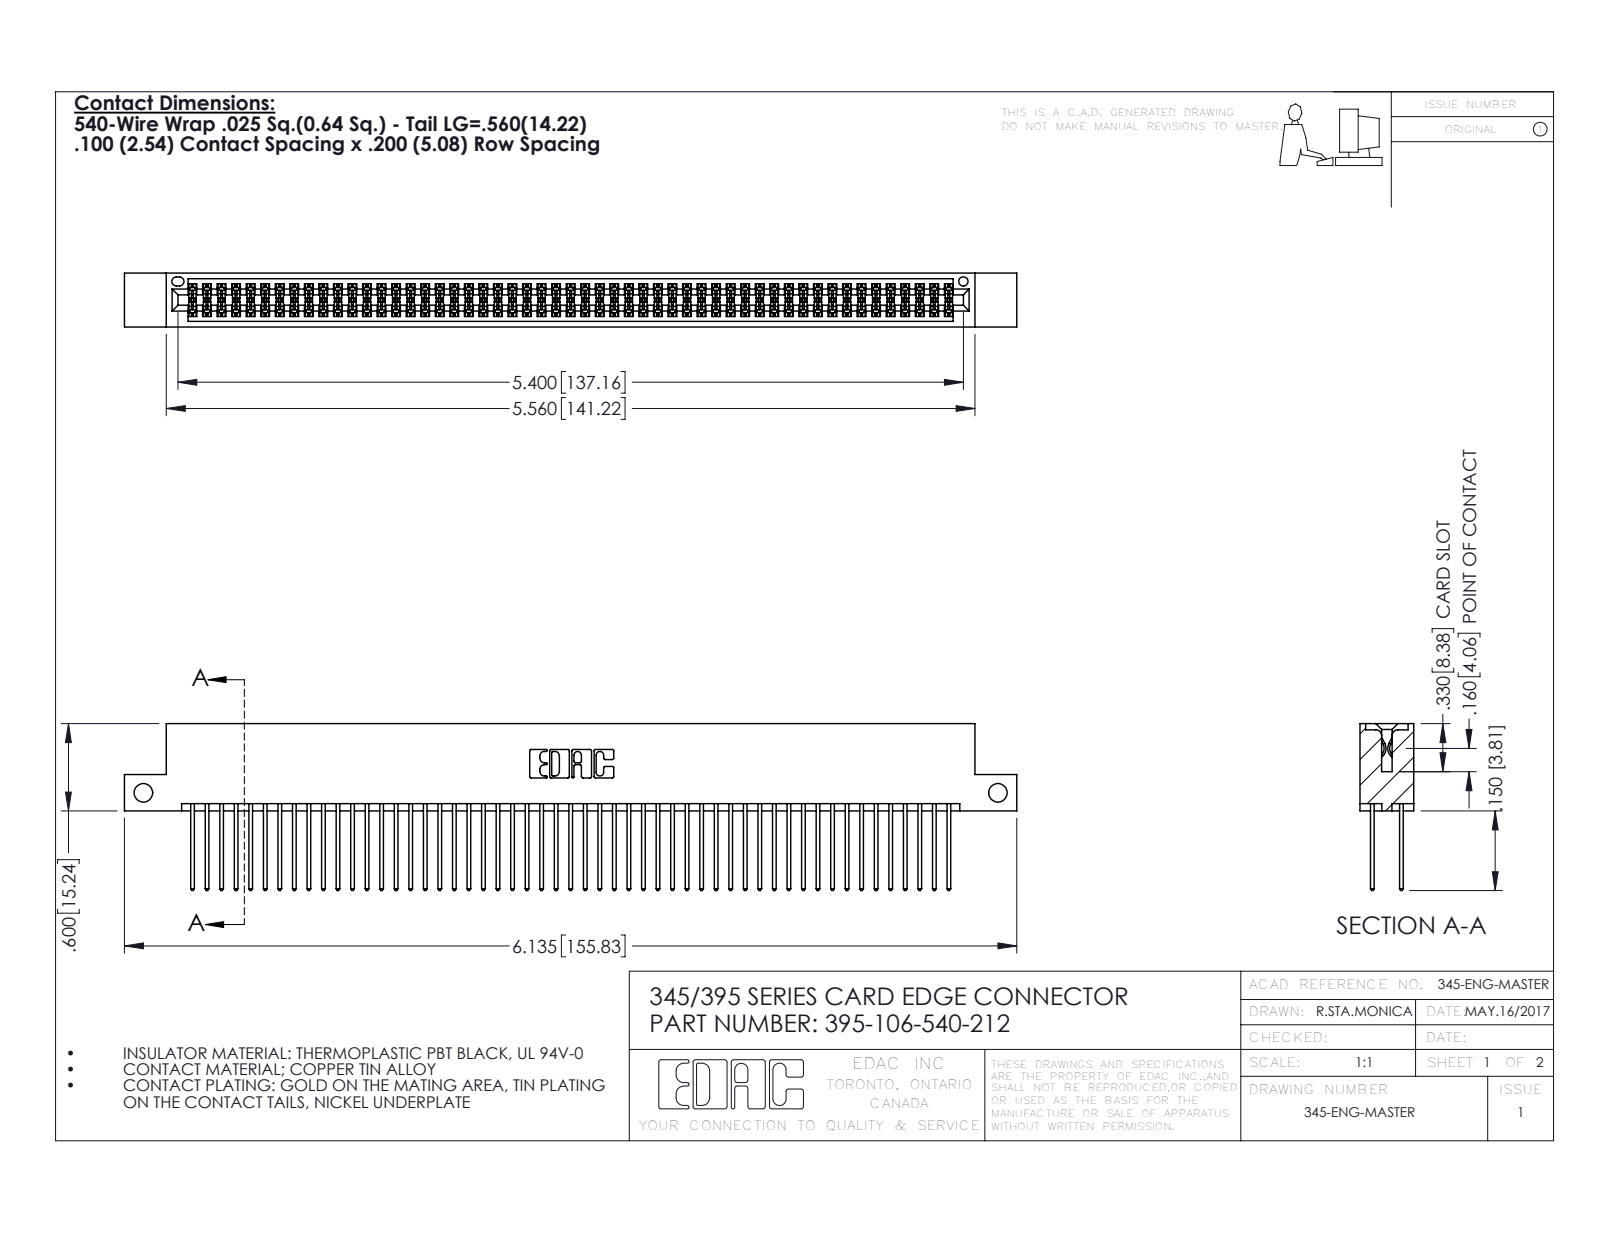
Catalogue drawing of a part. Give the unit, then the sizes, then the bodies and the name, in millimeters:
Units: millimetres
Overall size (bounding box): 155.8 × 29.1 × 9.4
Round holes (diameter × count): ⌀3.3 ×2, ⌀1.6 ×1
Partial cylindrical surfaces — rounded edges, fillets, slot ends (radius × count): R0.2 ×159, R0.3 ×106, R0.3 ×22, R0.2 ×6, R0.8 ×6, R0.7 ×3, R0.4 ×2, R0.5 ×2
Main face-to-face distances: 7.6, 1.8, 5.1, 2.5, 6.9, 0.6, 9.4, 5.7, 4.4, 3.8
Hole centre spacings: 149.2
Volume: 15 600 mm³ · Surface area: 24 940 mm²
Bodies: 107 solids, 5426 faces (3578 planar, 1848 cylindrical, 0 other)
Part name (STEP PRODUCT): 345-292-001_345-293-140; 395-106-540-212; 345 Part_Flush Mounting Lugs - Side Mount
STEP written by: SolidWorks 2016 (CONFIG_CONTROL_DESIGN)
